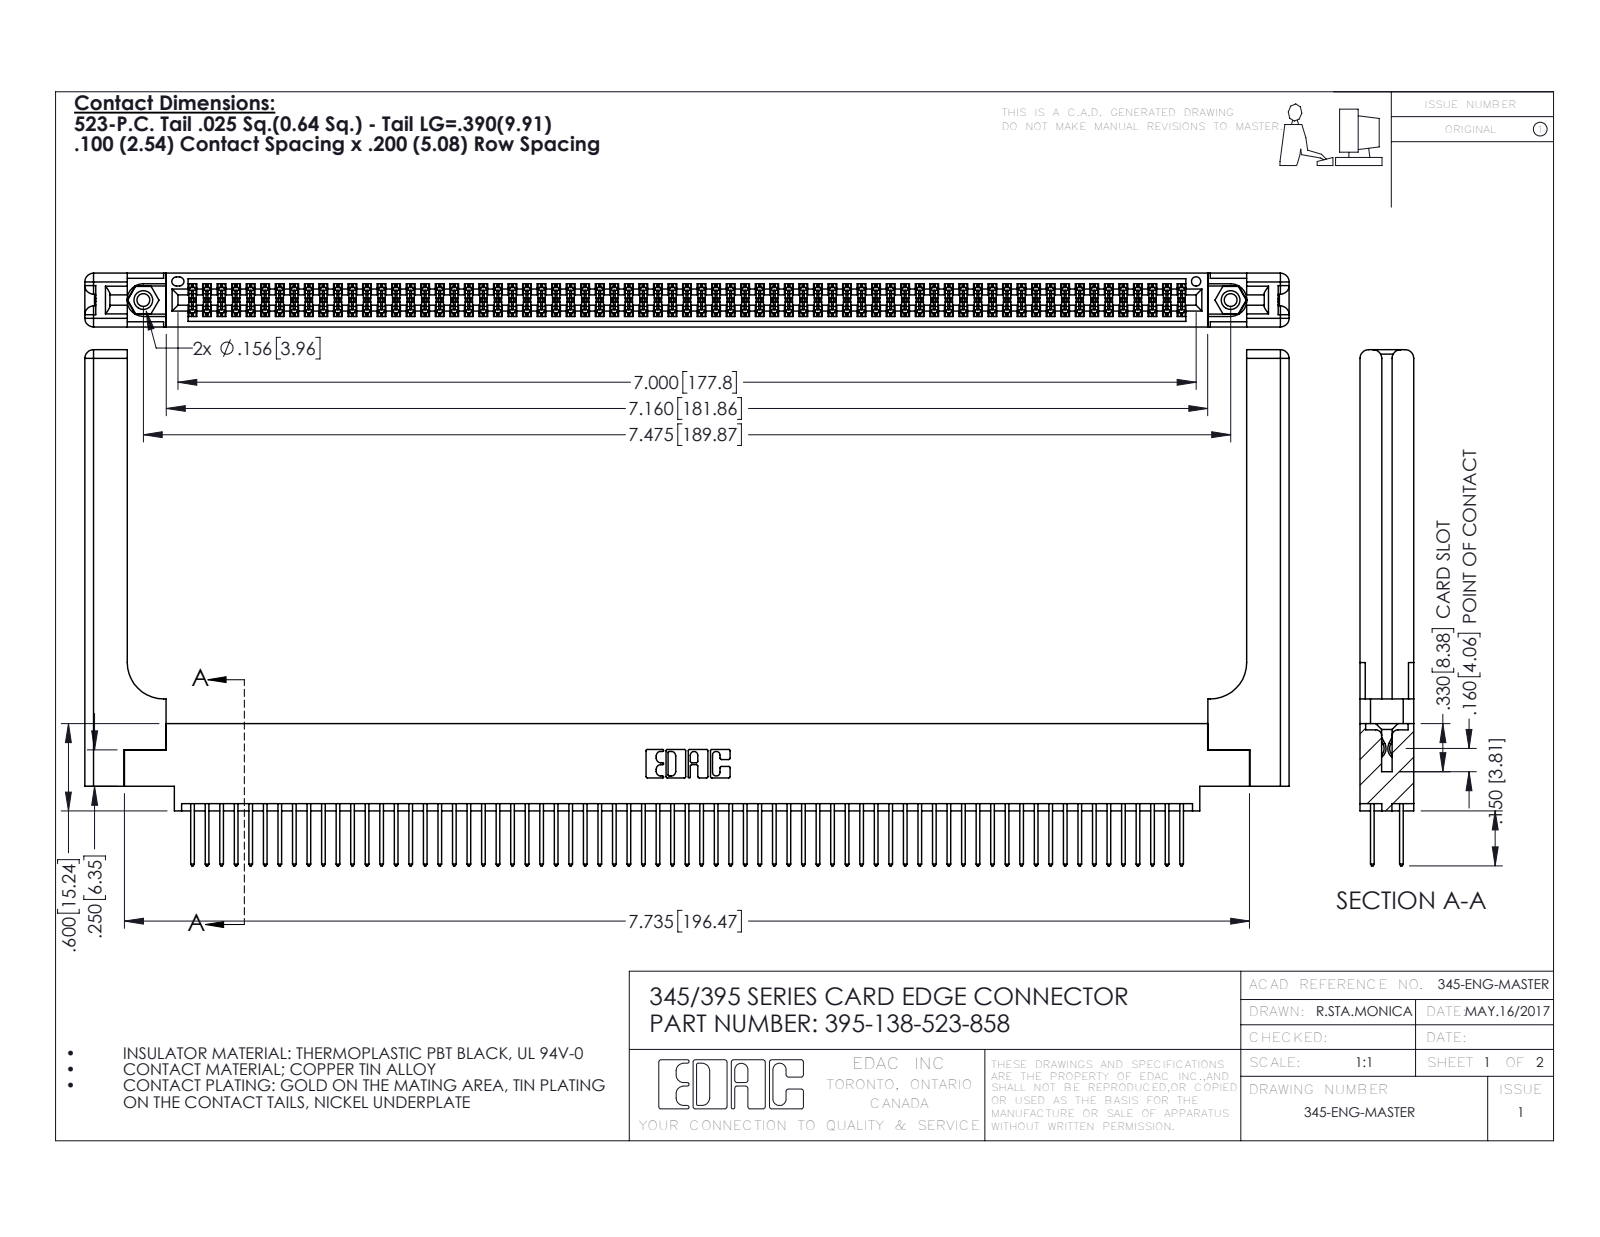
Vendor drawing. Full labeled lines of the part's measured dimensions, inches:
Part name (STEP PRODUCT): 345-250-001_345-250-001-102; 345-220-058_345-220-058; 345-292-001_345-293-123; 395-138-523-858 (+1 more)
STEP written by: SolidWorks 2016 (CONFIG_CONTROL_DESIGN)
Units: inches
Bodies: 143 solids, 7286 faces (4786 planar, 2440 cylindrical, 60 other)
Overall size (bounding box): 8.279 × 3.547 × 0.37
Volume: 1.789 in³ · Surface area: 58.61 in²
Round holes (diameter × count): ⌀0.089 ×2, ⌀0.125 ×2, ⌀0.156 ×2, ⌀0.064 ×1
Round bosses / shafts (diameter × count): ⌀0.155 ×2
Partial cylindrical surfaces — rounded edges, fillets, slot ends (radius × count): R0.006 ×207, R0.01 ×138, R0.01 ×22, R0.06 ×16, R0.007 ×6, R0.031 ×6, R0.026 ×3, R0.014 ×2
Main face-to-face distances: 0.072, 0.298, 0.37, 0.098, 0.272, 0.025, 0.2, 0.225, 0.175, 0.148
Hole centre spacings: 0.27, 7.239, 7.475
